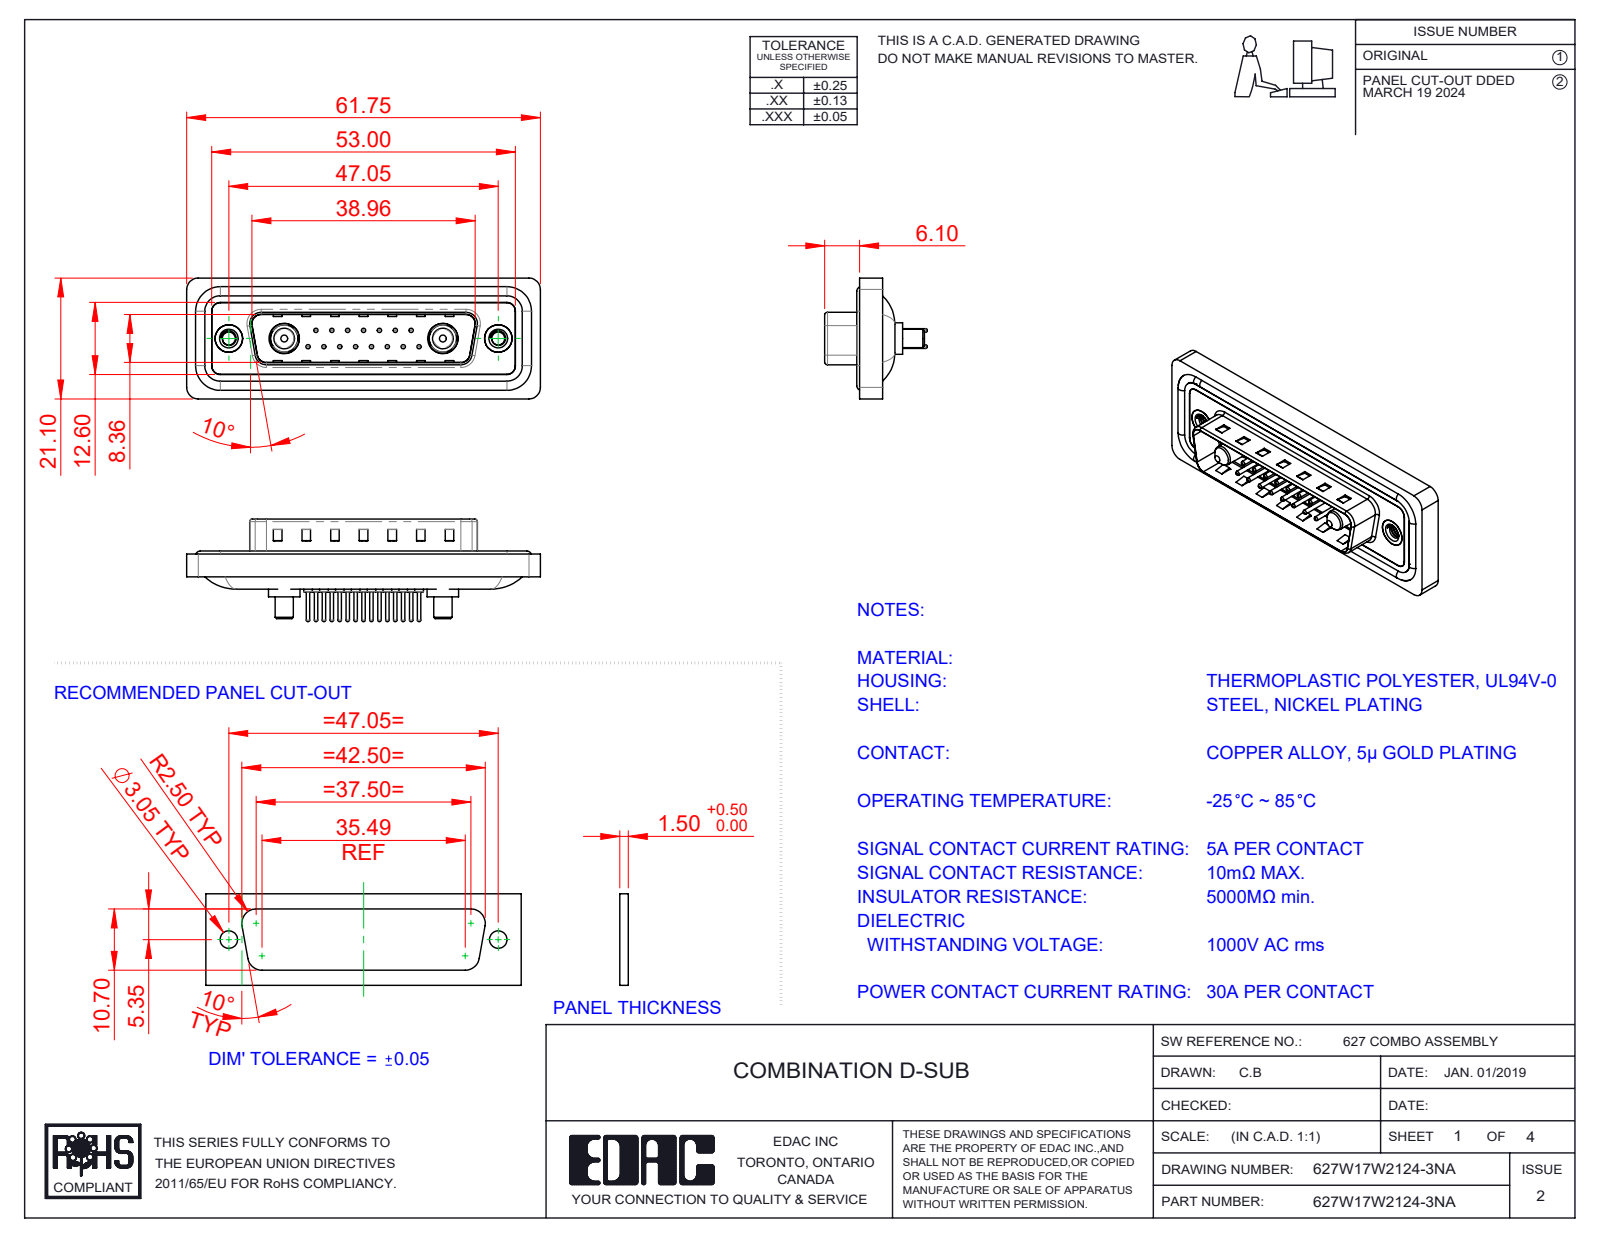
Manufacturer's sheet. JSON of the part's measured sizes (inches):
{"part_name": "627Combo Waterproof Housing_25 Contacts; 627Combo Contact Row 1_24; 627Combo Shell Rear_25 Contacts; 627Combo Threaded Rivet_A (+5 more)", "step_written_by": "SolidWorks 2023 (CONFIG_CONTROL_DESIGN)", "units": "inches", "bodies": {"solids": 26, "faces": 1114, "planar": 334, "cylindrical": 438, "other": 342}, "overall_size": [2.431, 0.831, 0.705], "volume_in3": 0.444, "surface_area_in2": 18.48, "round_holes": [[0.03, 15], [0.063, 15], [0.079, 15], [0.089, 2], [0.157, 2], [0.189, 2], [0.191, 2], [0.197, 2], [0.209, 2]], "round_bosses_or_shafts": [[0.059, 15], [0.024, 15], [0.063, 4], [0.217, 2], [0.205, 2], [0.193, 2], [0.187, 2], [0.148, 2]], "partial_cylinders_radius": [[0.059, 22], [0.079, 18], [0.02, 8], [0.063, 8], [0.01, 4], [0.024, 4], [0.026, 4], [0.035, 4]], "face_to_face_distances": [0.016, 0.059, 0.043, 0.063, 0.02, 0.122, 0.114, 0.032, 0.377, 0.161], "hole_center_spacings": [0.124, 0.109, 0.218, 0.327, 0.198, 0.295, 0.436, 0.198]}
